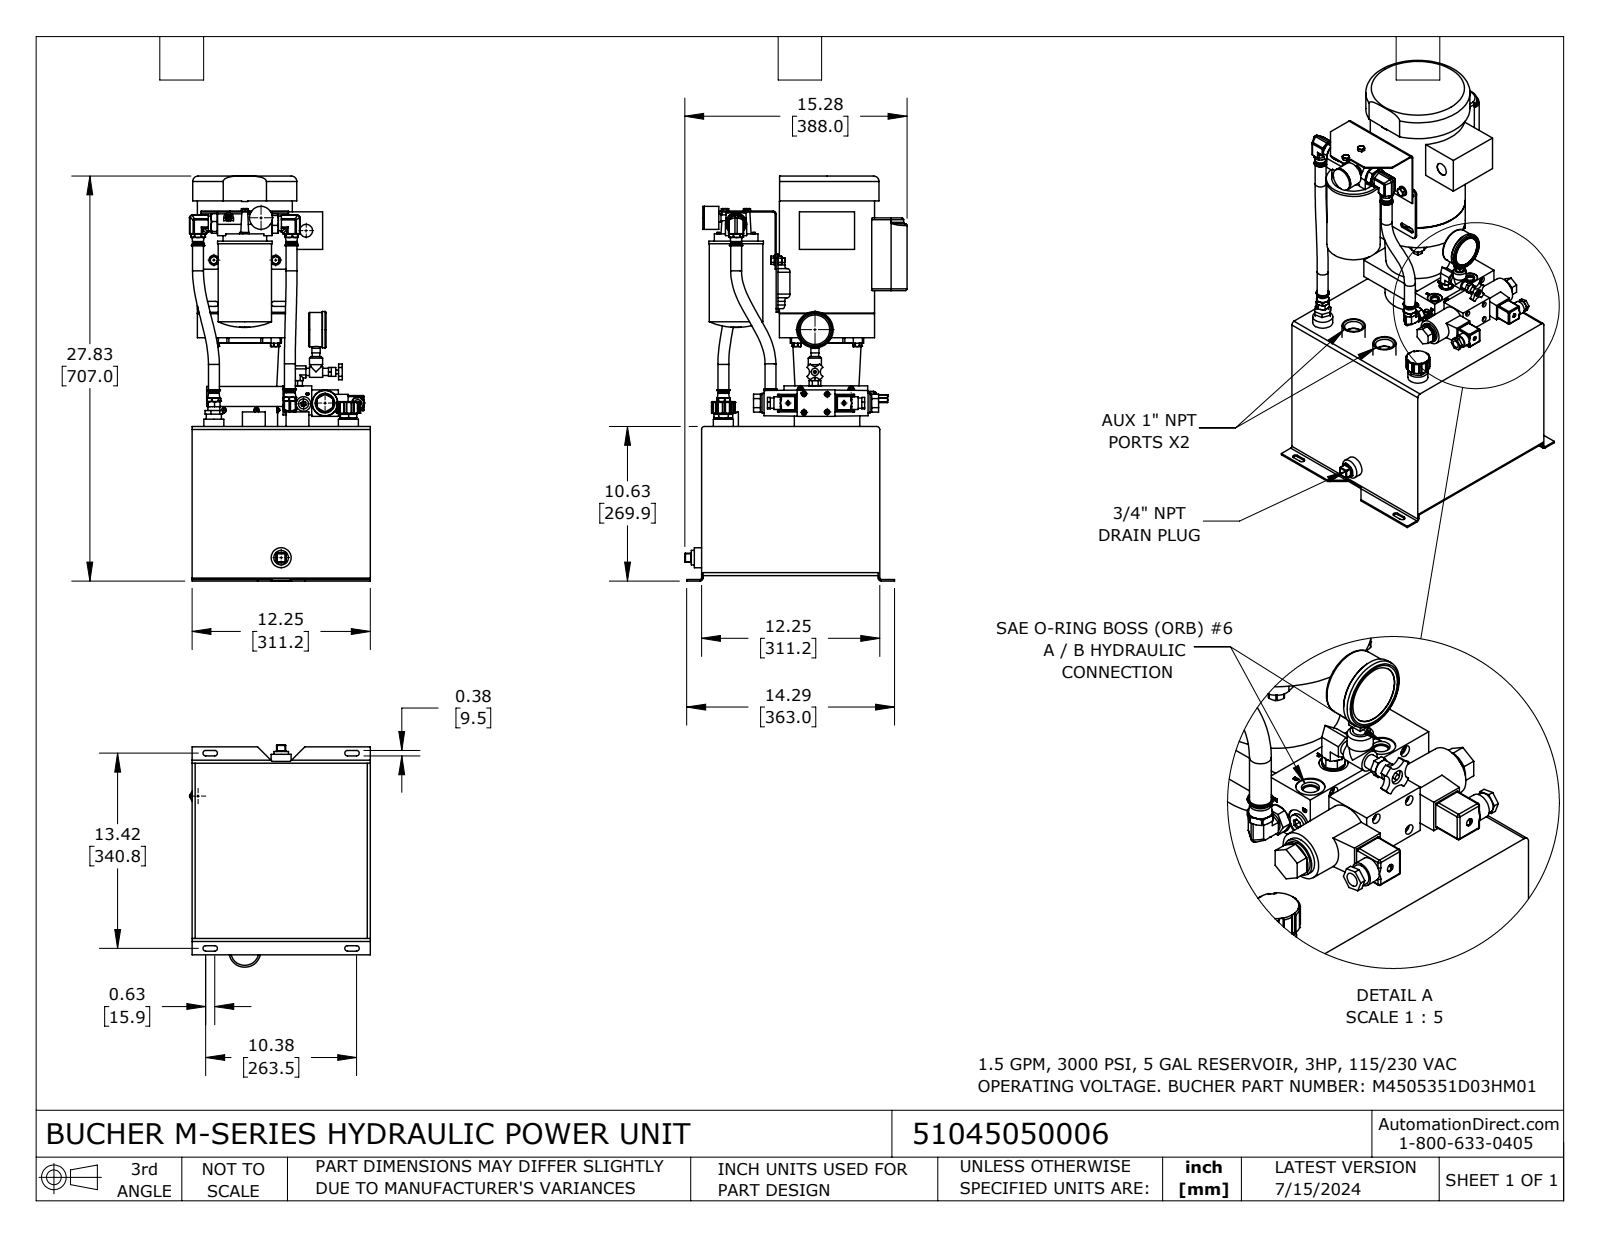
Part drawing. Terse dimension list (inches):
name: 51045050006
written by: SolidWorks 2023 (CONFIG_CONTROL_DESIGN)
unit: in
bodies: 61 solids, 2997 faces (1246 planar, 999 cylindrical, 752 other)
size: 27.833 × 15.275 × 12.421
volume: 761.1 in³; area: 3 001 in²
holes: 9× ⌀1, 8× ⌀0.313, 8× ⌀0.469, 8× ⌀0.511, 6× ⌀0.225, 5× ⌀0.25, 5× ⌀0.281, 4× ⌀0.17, 4× ⌀0.203, 4× ⌀0.228, 4× ⌀0.266, 4× ⌀0.291
bosses: 6× ⌀0.367, 6× ⌀0.187, 5× ⌀0.9, 5× ⌀0.75, 4× ⌀0.738, 4× ⌀0.68, 4× ⌀0.46, 4× ⌀0.37
rounds: 24× R0.025, 24× R0.039, 24× R0.05, 20× R0.02, 16× R0.25, 14× R0.07, 13× R0.12, 12× R0.04
face distances: 0.104, 12.146, 12.25, 12.041, 10.25, 10.146, 0.105, 10.145, 10.041, 5.125
hole spacings: 4.381, 2.937, 1.575, 1.781, 1.781, 2.098, 2.098, 4.154
